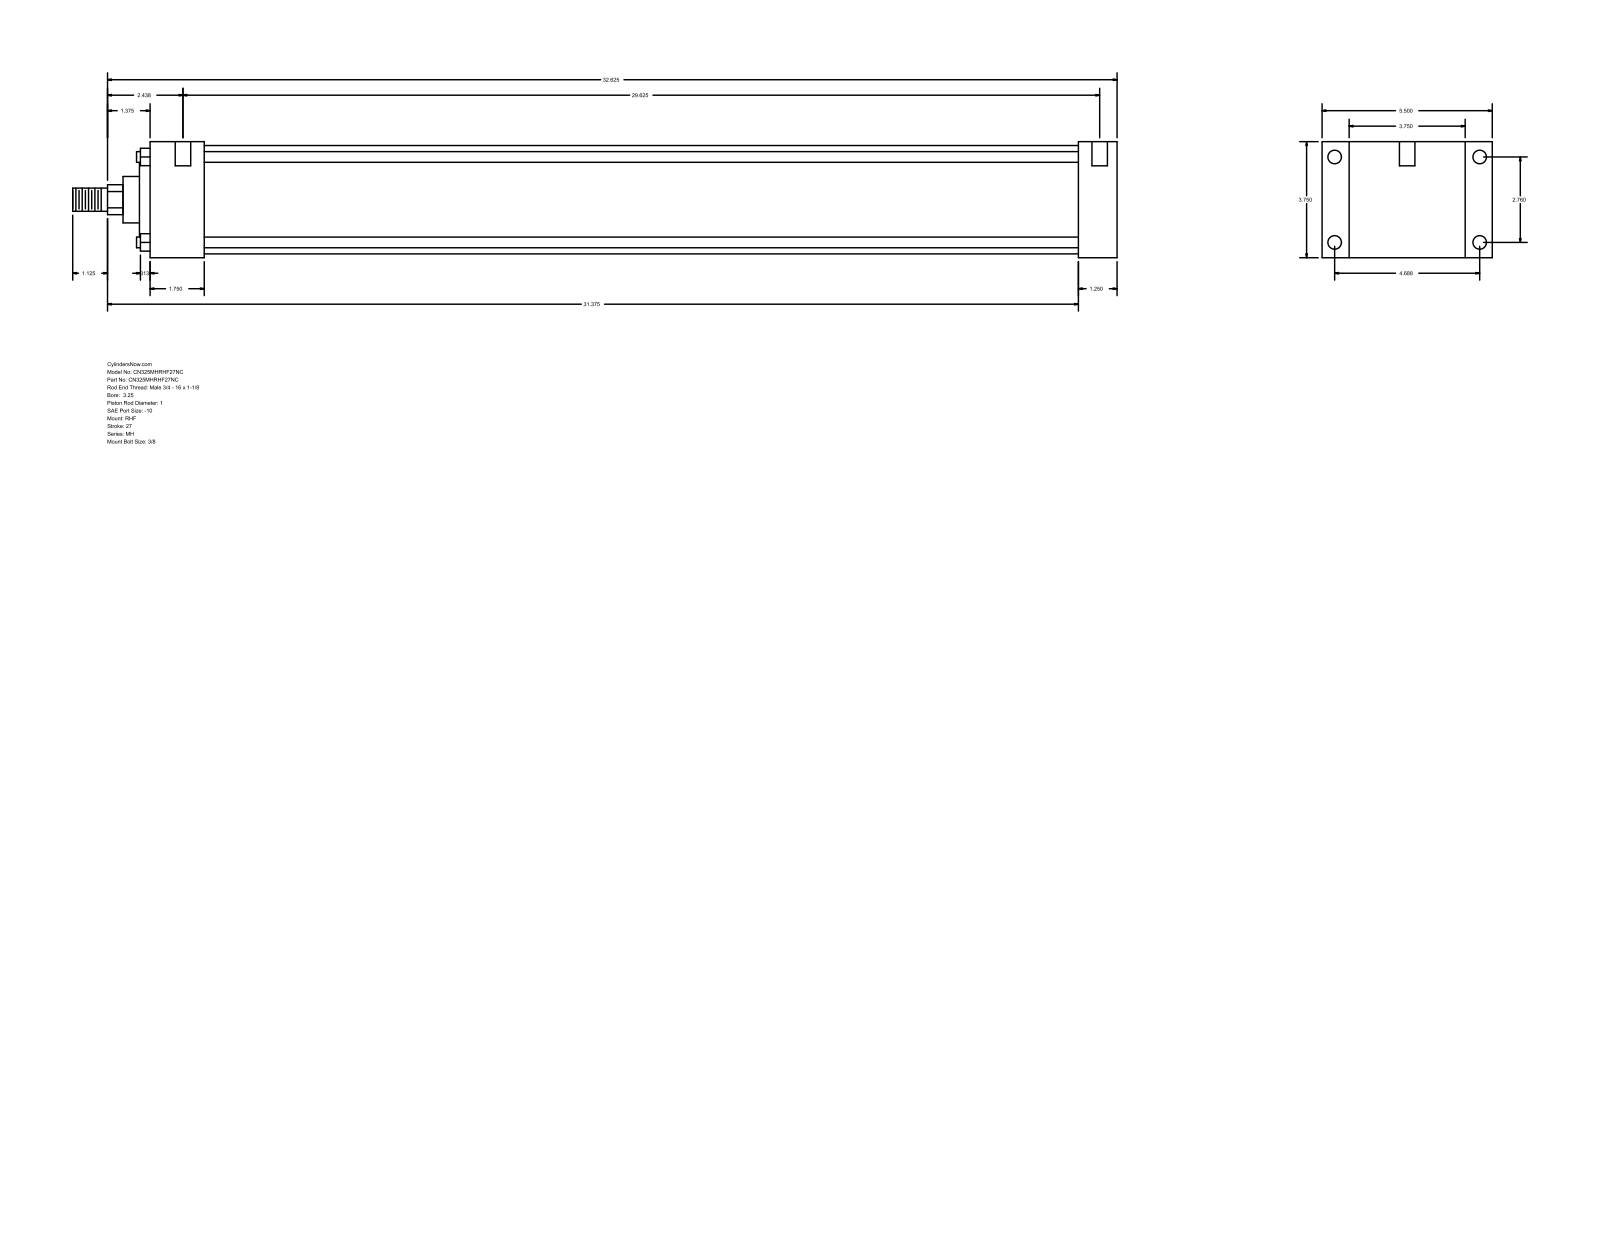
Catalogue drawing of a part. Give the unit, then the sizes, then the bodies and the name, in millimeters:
Units: millimetres
Overall size (bounding box): 857.25 × 139.7 × 95.25
Round holes (diameter × count): ⌀5.56 ×4, ⌀11.13 ×4, ⌀12.7 ×2
Round bosses / shafts (diameter × count): ⌀8.76 ×4, ⌀88.9 ×1, ⌀60.33 ×1, ⌀38.1 ×1, ⌀25.4 ×1, ⌀19.05 ×1
Partial cylindrical surfaces — rounded edges, fillets, slot ends (radius × count): R12.29 ×1
Main face-to-face distances: 95.24, 31.75, 22.23, 117.47, 762, 793.75, 139.7, 44.46, 717.54, 749.29
Hole centre spacings: 70.1, 119.06, 138.16, 758.82, 1.58, 4.76, 752.48, 754.06
Bodies: 0 solids, 90 faces (61 planar, 29 cylindrical, 0 other)
Part name (STEP PRODUCT): MH_RHF__0325_1
STEP written by: GSSL Pune (CONFIG_CONTROL_DESIGN)
